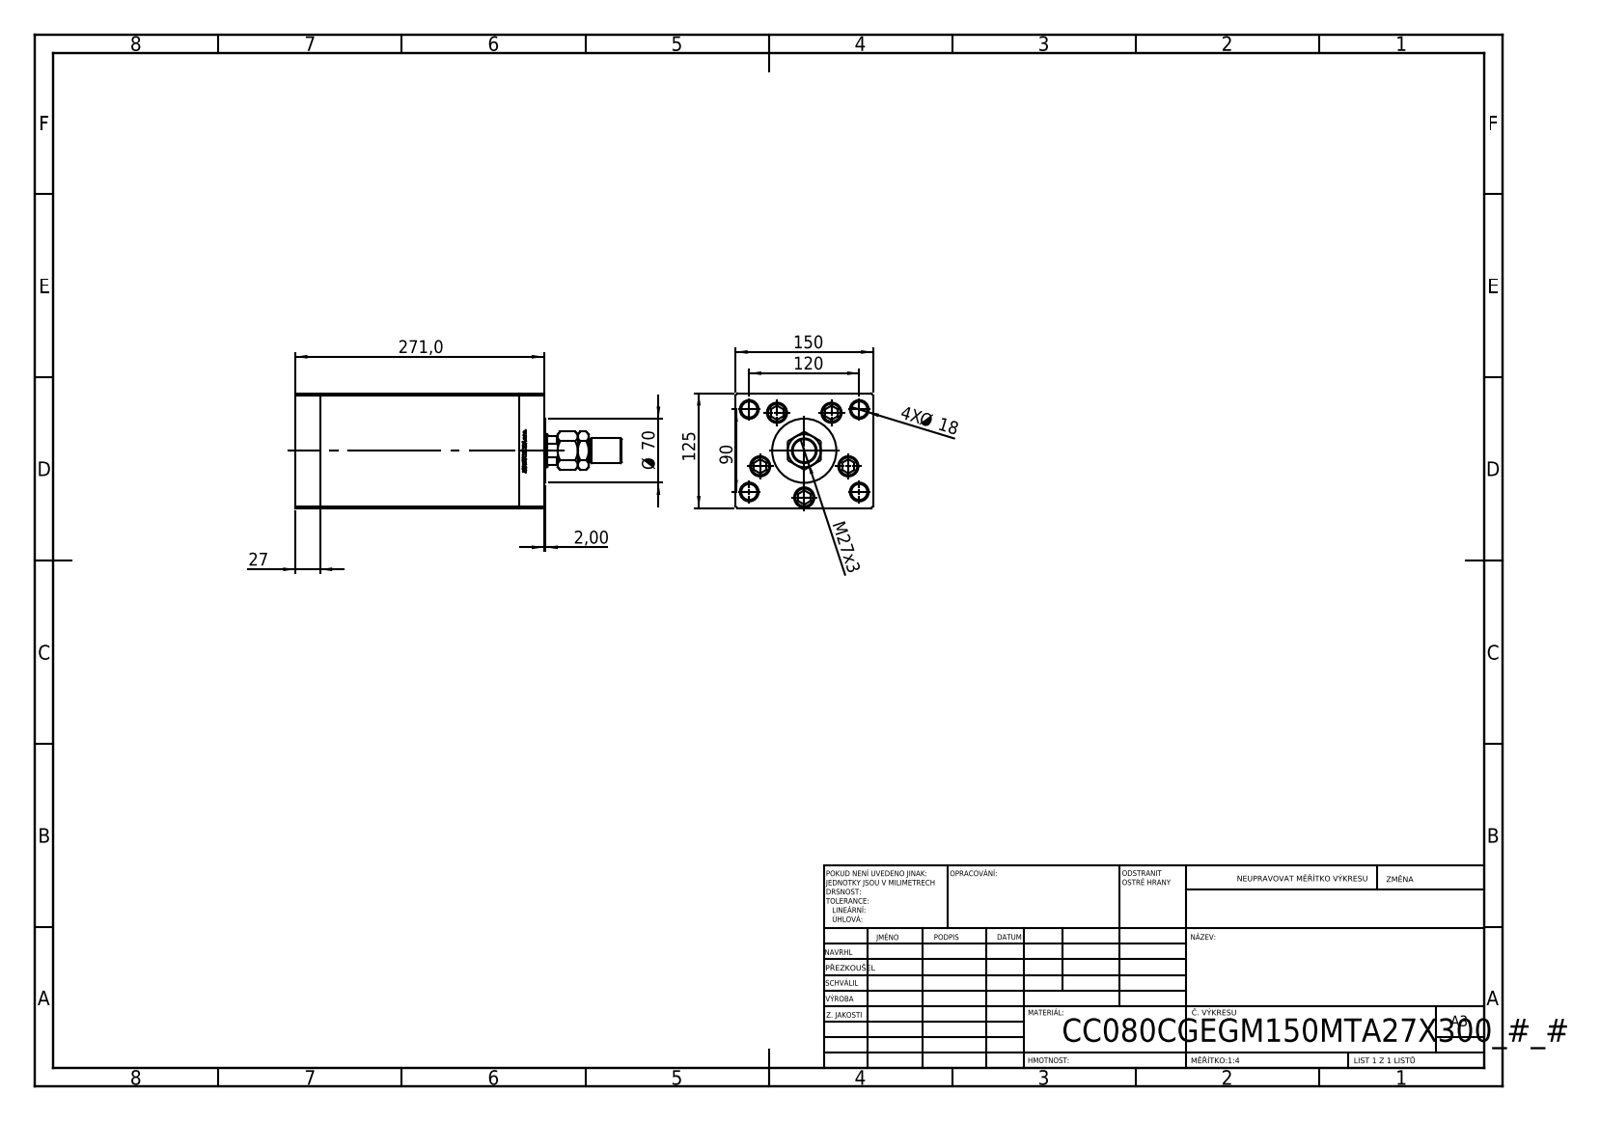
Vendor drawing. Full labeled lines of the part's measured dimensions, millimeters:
Part name (STEP PRODUCT): V220C_VC_C; ALLEN BOLT; MTA; V220C_C MIDDLE (+2 more)
STEP written by: SolidWorks 2019 (CONFIG_CONTROL_DESIGN)
Units: millimetres
Bodies: 14 solids, 1212 faces (557 planar, 163 cylindrical, 492 other)
Overall size (bounding box): 356 × 150 × 125
Volume: 4 186 000 mm³ · Surface area: 459 325 mm²
Round holes (diameter × count): ⌀17.5 ×9, ⌀22 ×5, ⌀16 ×4, ⌀20.5 ×4, ⌀21 ×1, ⌀25.5 ×1, ⌀36 ×1
Round bosses / shafts (diameter × count): ⌀8 ×5, ⌀21 ×4, ⌀80 ×1, ⌀70 ×1, ⌀27 ×1, ⌀25 ×1
Partial cylindrical surfaces — rounded edges, fillets, slot ends (radius × count): R0.93 ×2, R17.5 ×1
Main face-to-face distances: 150, 125, 27, 244, 217, 33.5, 6.5, 271, 237.5, 210.5
Hole centre spacings: 51, 75, 30.43, 30.48, 58.89, 60.3, 61.25, 63.14
